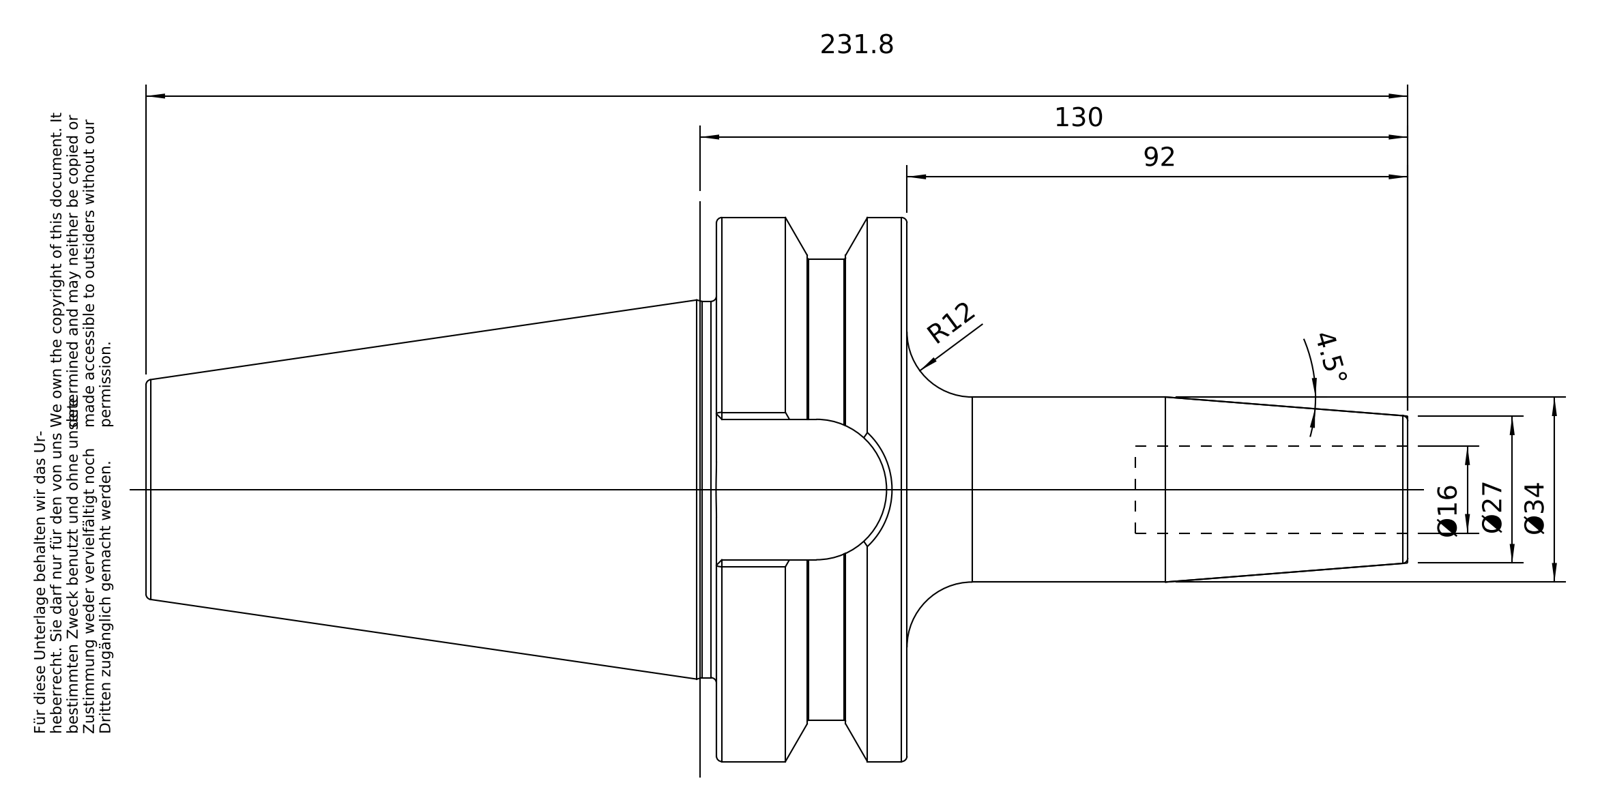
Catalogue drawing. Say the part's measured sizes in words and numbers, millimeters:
The part is named "50-644-16". Its 3-D file was written by "PRO/ENGINEER BY PARAMETRIC TECHNOLOGY CORPORATION, 2010430 (CONFIG_CONTROL_DESIGN)". It is 1 solid with 96 faces: 26 planar, 22 cylindrical and 48 other. Overall it measures 231.8 by 99.97 by 99.97 millimeters. Its volume is 537 586 cubic millimeters and its surface area 62 860 square millimeters. Round holes: 1 of diameter 16, 1 of diameter 20.75, 1 of diameter 25.02, 1 of diameter 25.7. Round bosses or shafts: 1 of diameter 99.97, 1 of diameter 84.75, 1 of diameter 69.15, 1 of diameter 34, 1 of diameter 24.01. Partial cylindrical surfaces (rounded edges, fillets, slot ends): 1 of radius 12.9. The main face-to-face distances are 35, 70.4, 104.8, 139.8, 25.8, 231.8, 127, 92, 181.8, 77.
